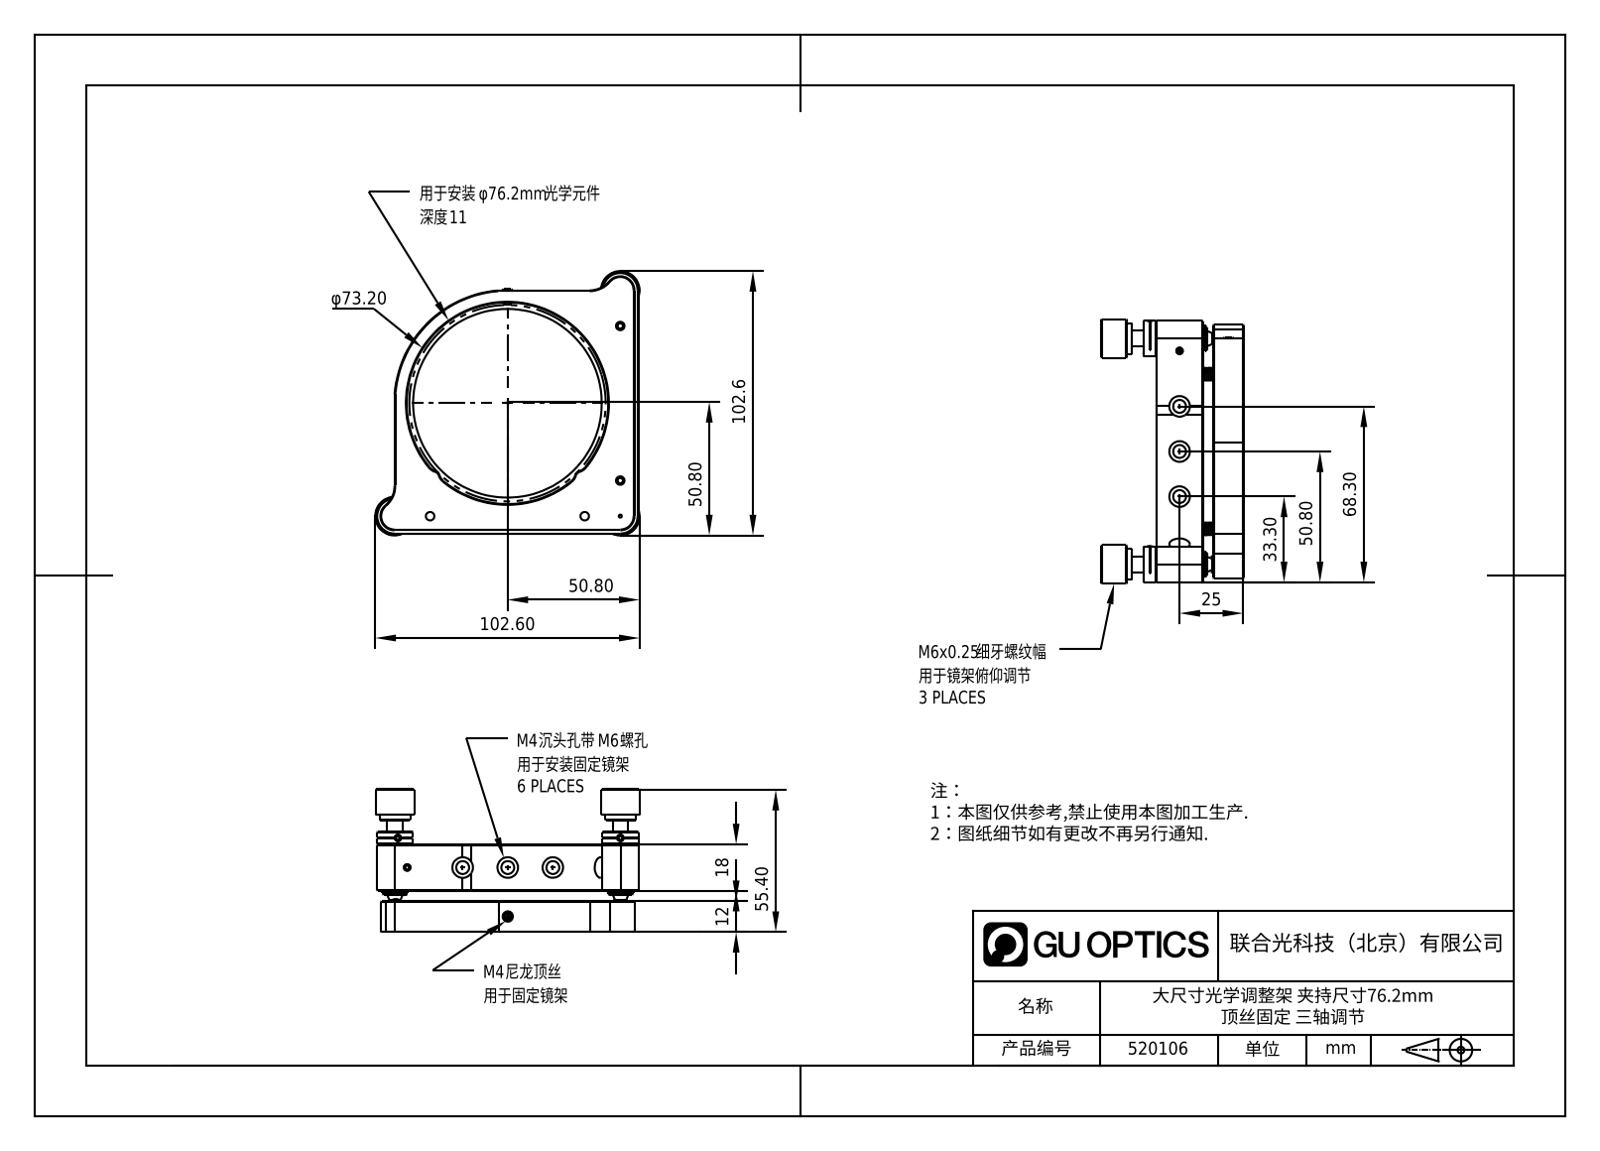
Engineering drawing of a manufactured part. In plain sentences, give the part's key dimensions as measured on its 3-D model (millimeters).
The part is named "520106". Its 3-D file was written by "SolidWorks 2020 (CONFIG_CONTROL_DESIGN)". It is 0 solids with 329 faces: 152 planar, 88 cylindrical and 89 other. Overall it measures 102.6 by 102.6 by 55.5 millimeters. Round holes: 6 of diameter 5, 6 of diameter 8, 4 of diameter 6.5, 3 of diameter 9.5, 1 of diameter 4. Round bosses or shafts: 5 of diameter 3.3, 3 of diameter 15, 3 of diameter 14, 3 of diameter 6, 3 of diameter 4, 3 of diameter 3, 2 of diameter 8, 2 of diameter 2. Partial cylindrical surfaces (rounded edges, fillets, slot ends): 8 of radius 1.05, 7 of radius 5, 4 of radius 10, 3 of radius 5.5, 2 of radius 2.5, 1 of radius 0.2, 1 of radius 40, 1 of radius 43.94. The main face-to-face distances are 12, 22, 34, 18, 16, 4, 1.5, 1, 5, 23. The hole center spacings are 13.8, 17.5, 73.8, 35, 60, 75.08, 87.6, 88.68.
